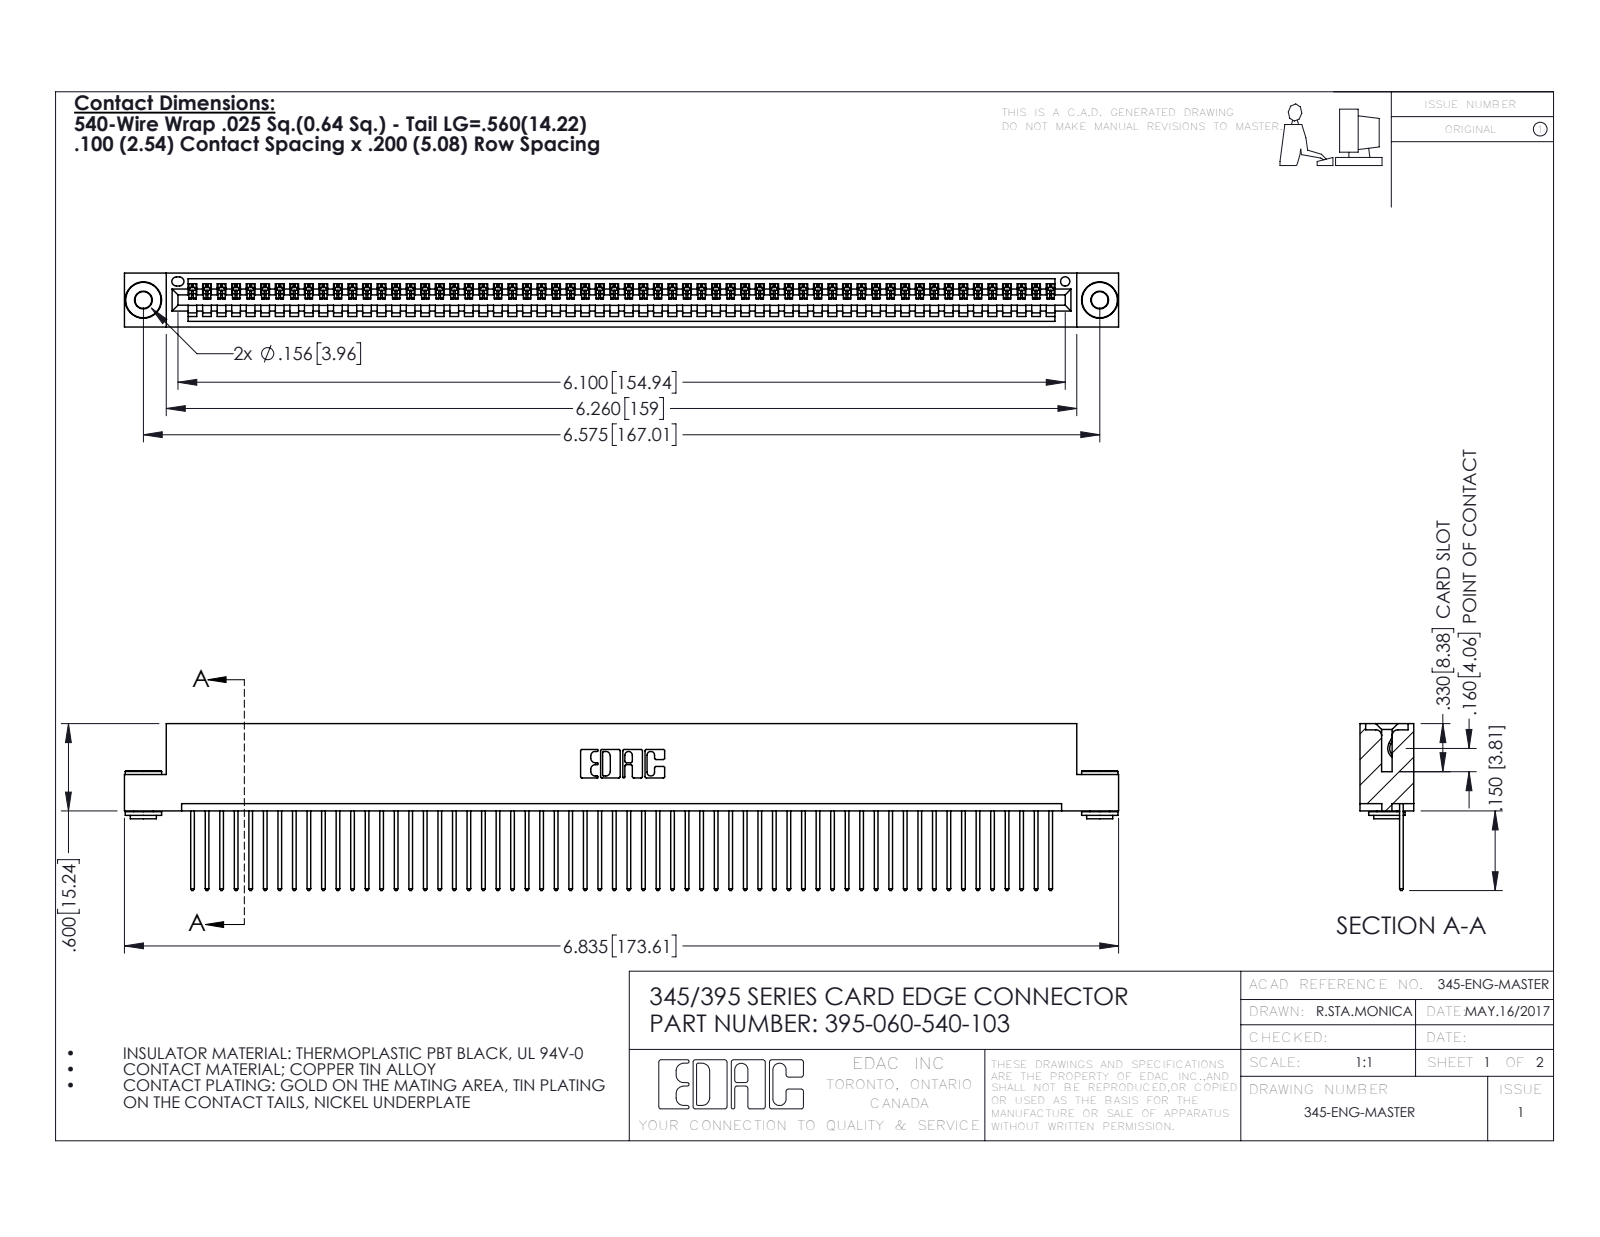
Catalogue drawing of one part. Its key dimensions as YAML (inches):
part_name: "345-250-002_345-250-002-102; 395-060-540-103; 345-292-001_345-293-140; 345 Part_Flush Mounting Lugs - 0.156 Dia-TH"
step_written_by: "SolidWorks 2016 (CONFIG_CONTROL_DESIGN)"
units: inches
bodies: {solids: 63, faces: 3644, planar: 2490, cylindrical: 1146, other: 8}
overall_size: [6.835, 1.147, 0.37]
volume: 1.021
surface_area: 36.09
round_holes:
  - {diameter: 0.116, count: 2}
  - {diameter: 0.156, count: 2}
  - {diameter: 0.064, count: 1}
round_bosses_or_shafts:
  - {diameter: 0.25, count: 2}
  - {diameter: 0.18, count: 2}
  - {diameter: 0.136, count: 2}
partial_cylinders:
  - {radius: 0.006, count: 120}
  - {radius: 0.01, count: 120}
  - {radius: 0.01, count: 22}
  - {radius: 0.007, count: 6}
  - {radius: 0.031, count: 6}
  - {radius: 0.026, count: 3}
  - {radius: 0.031, count: 2}
  - {radius: 0.04, count: 2}
face_to_face_distances: [0.072, 0.298, 0.37, 0.025, 0.098, 0.272, 0.2, 0.225, 0.149, 0.072]
hole_center_spacings: [0.27, 6.339, 6.575]
